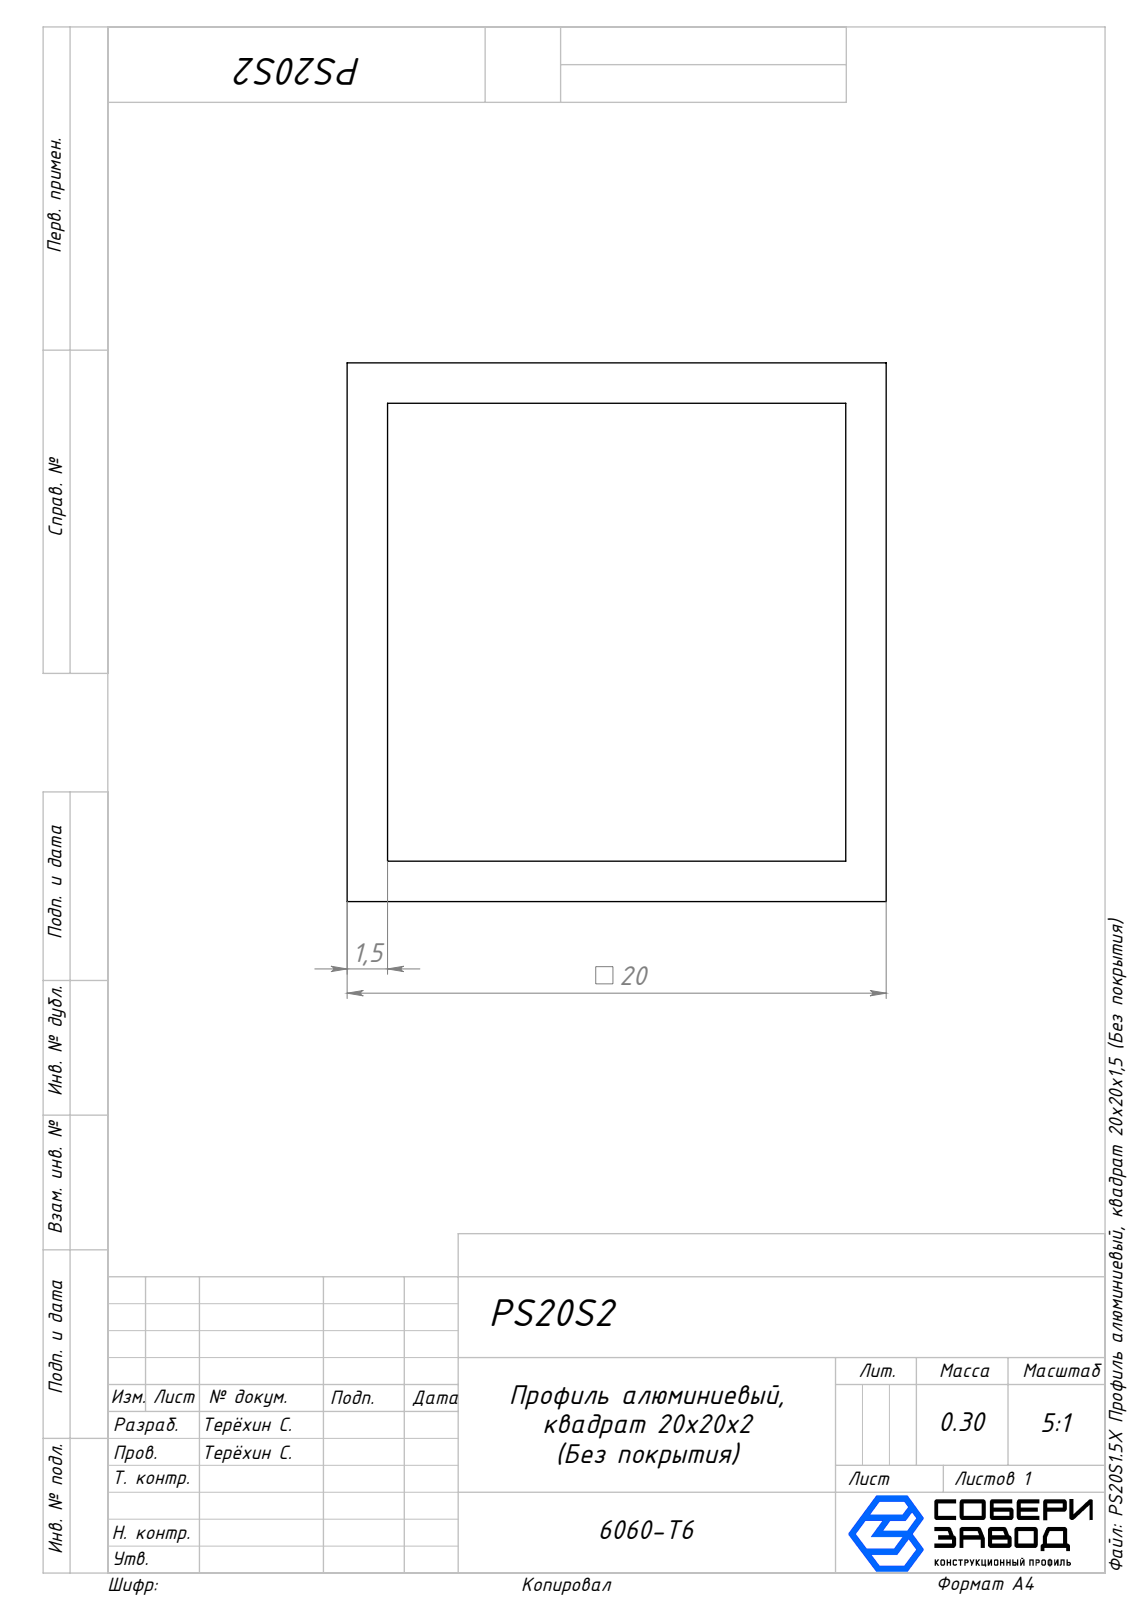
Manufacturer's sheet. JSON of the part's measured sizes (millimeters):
{"part_name": "PS20S1.5X Профиль алюминиевый, квадрат 20x20x1,5 (Без покрытия)", "step_written_by": "SolidWorks 2024 (AUTOMOTIVE_DESIGN)", "units": "millimeters", "bodies": {"solids": 1, "faces": 10, "planar": 10, "cylindrical": 0, "other": 0}, "overall_size": [1000, 20, 20], "volume_mm3": 111000, "surface_area_mm2": 148222, "face_to_face_distances": [1.5, 18.5, 20, 17, 1000]}
